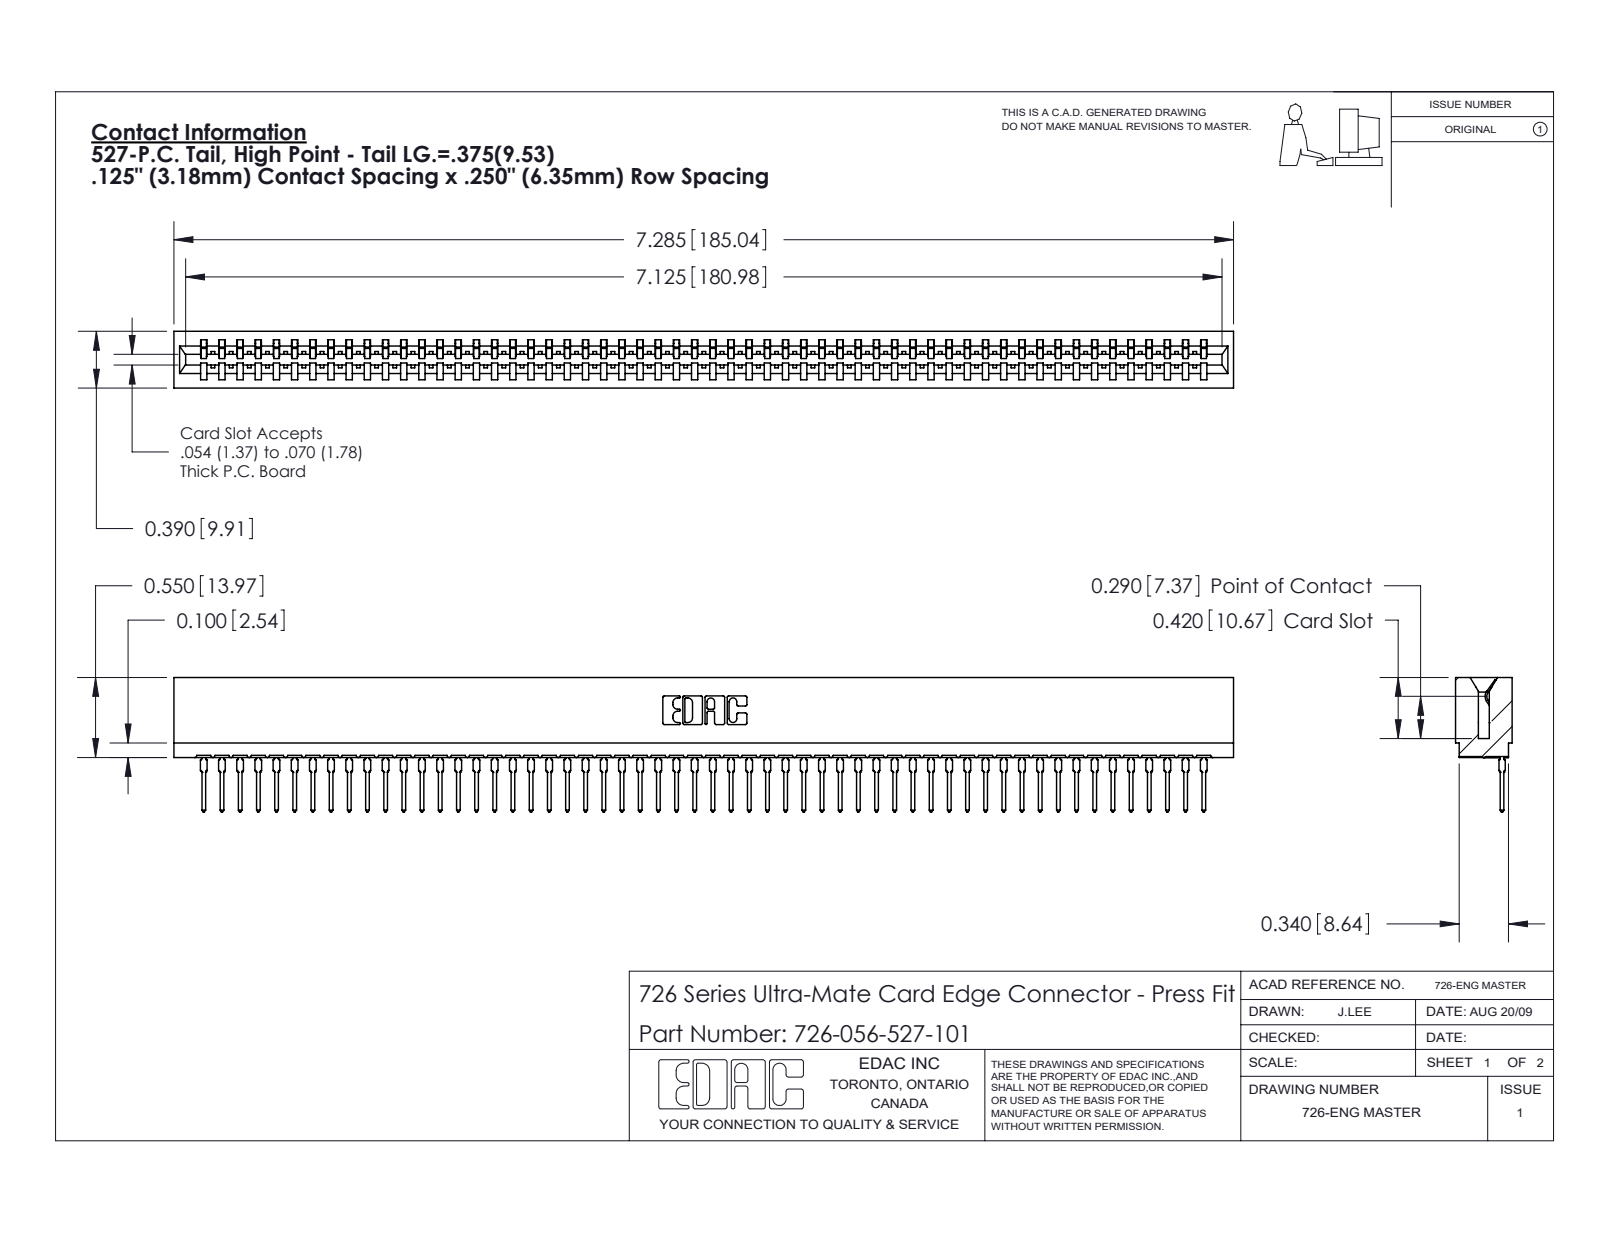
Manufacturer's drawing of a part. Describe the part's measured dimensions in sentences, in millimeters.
The part is named "746-292-001_527; 726 Part_.515 Slot Depth - 01; 726-056-527-101". Its 3-D file was written by "SolidWorks 2020 (CONFIG_CONTROL_DESIGN)". It is 57 solids with 6145 faces: 3583 planar, 1106 cylindrical and 1456 other. Overall it measures 185 by 23.5 by 9.9 millimeters. Its volume is 16 500 cubic millimeters and its surface area 25 700 square millimeters. Partial cylindrical surfaces (rounded edges, fillets, slot ends): 112 of radius 0.5, 57 of radius 0.4, 22 of radius 0.3, 6 of radius 0.2, 6 of radius 0.8, 4 of radius 0.1, 4 of radius 0.3, 3 of radius 0.7. The main face-to-face distances are 1.4, 8.5, 9.9, 0.6, 7.8, 6.4, 7, 2.1, 9.3, 0.8.
